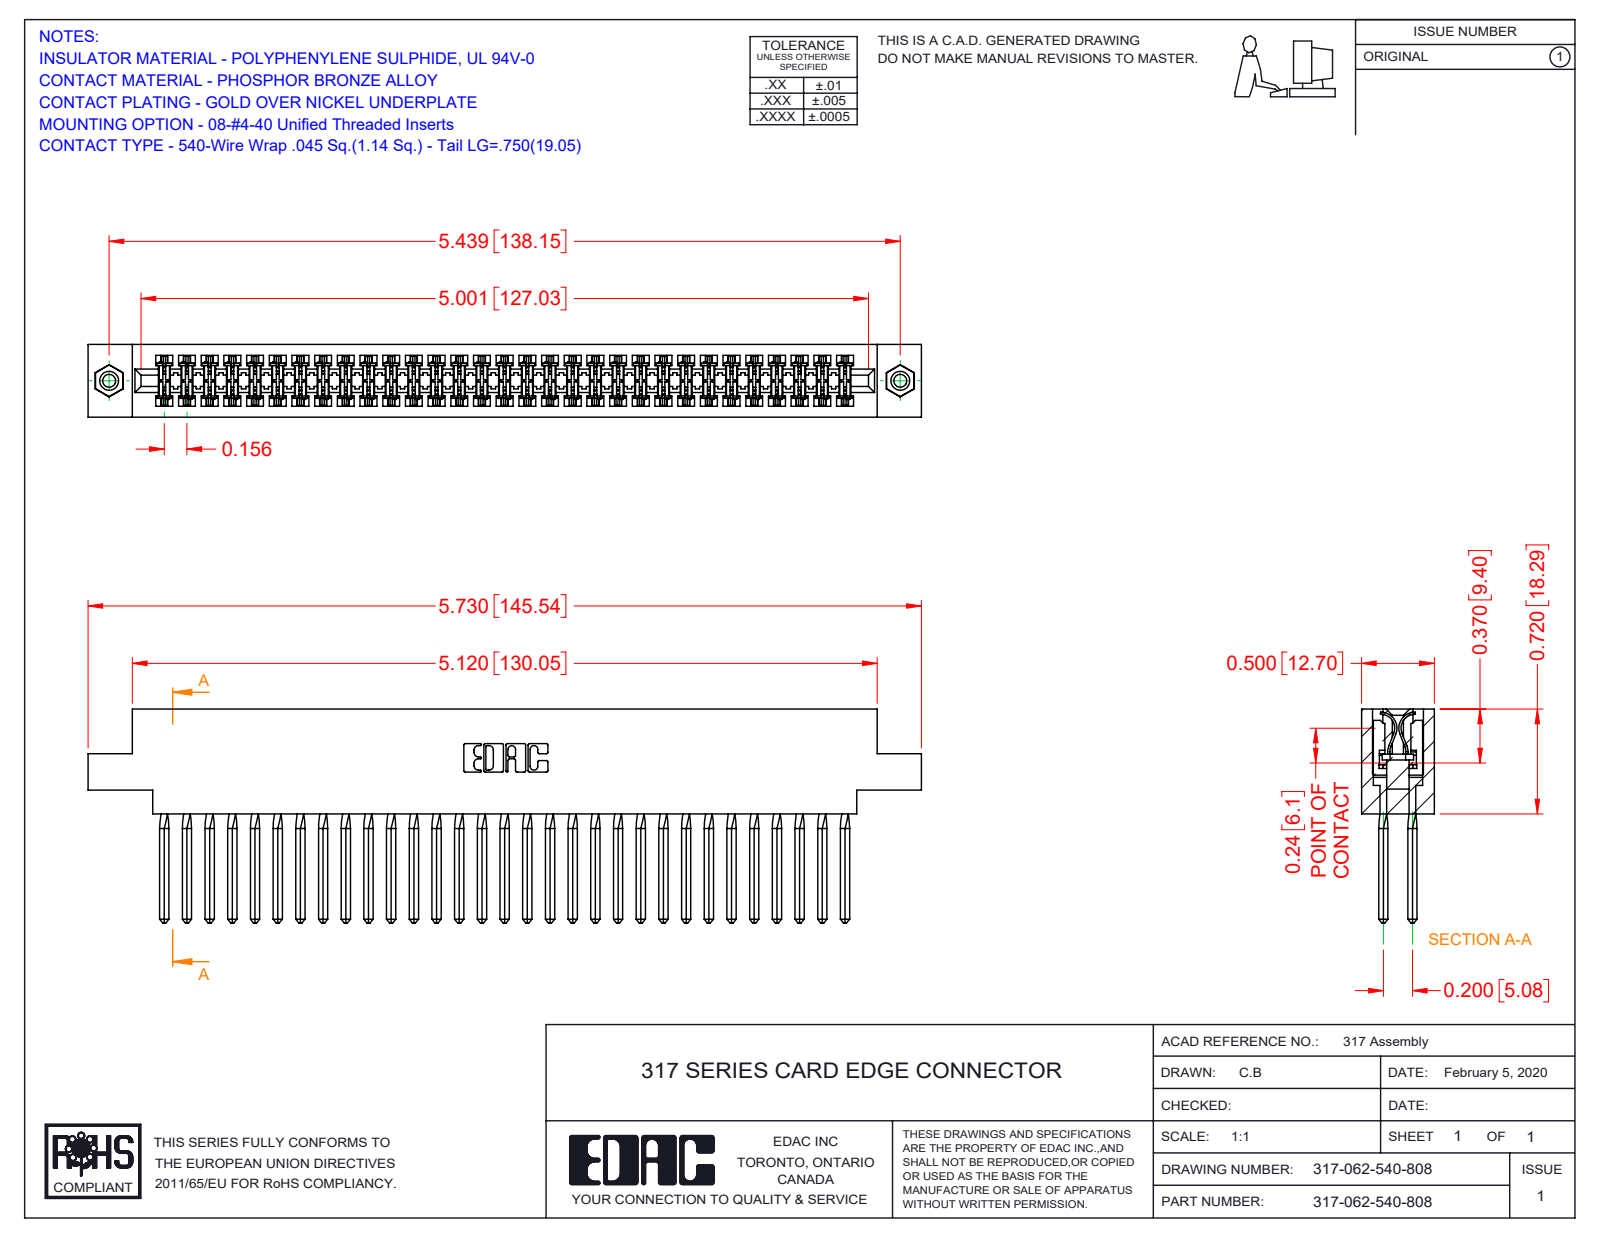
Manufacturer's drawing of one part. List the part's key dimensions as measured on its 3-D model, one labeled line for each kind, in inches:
Part name (STEP PRODUCT): 317 Part_.156 Dia - TI; 317-290-001_540; 345-250-001_345-250-003-102; 317-062-540-878
STEP written by: SolidWorks 2016 (CONFIG_CONTROL_DESIGN)
Units: inches
Bodies: 65 solids, 5680 faces (4616 planar, 800 cylindrical, 264 other)
Overall size (bounding box): 5.73 × 1.47 × 0.5
Volume: 1.468 in³ · Surface area: 54.96 in²
Round holes (diameter × count): ⌀0.089 ×2, ⌀0.125 ×2, ⌀0.156 ×2
Round bosses / shafts (diameter × count): ⌀0.155 ×2
Partial cylindrical surfaces — rounded edges, fillets, slot ends (radius × count): R0.015 ×124, R0.01 ×22, R0.007 ×6, R0.031 ×6, R0.026 ×3, R0.095 ×2, R0.1 ×2, R0.11 ×2
Main face-to-face distances: 0.5, 0.075, 0.425, 0.35, 0.11, 0.195, 0.094, 0.2, 0.115, 0.131
Hole centre spacings: 5.439
